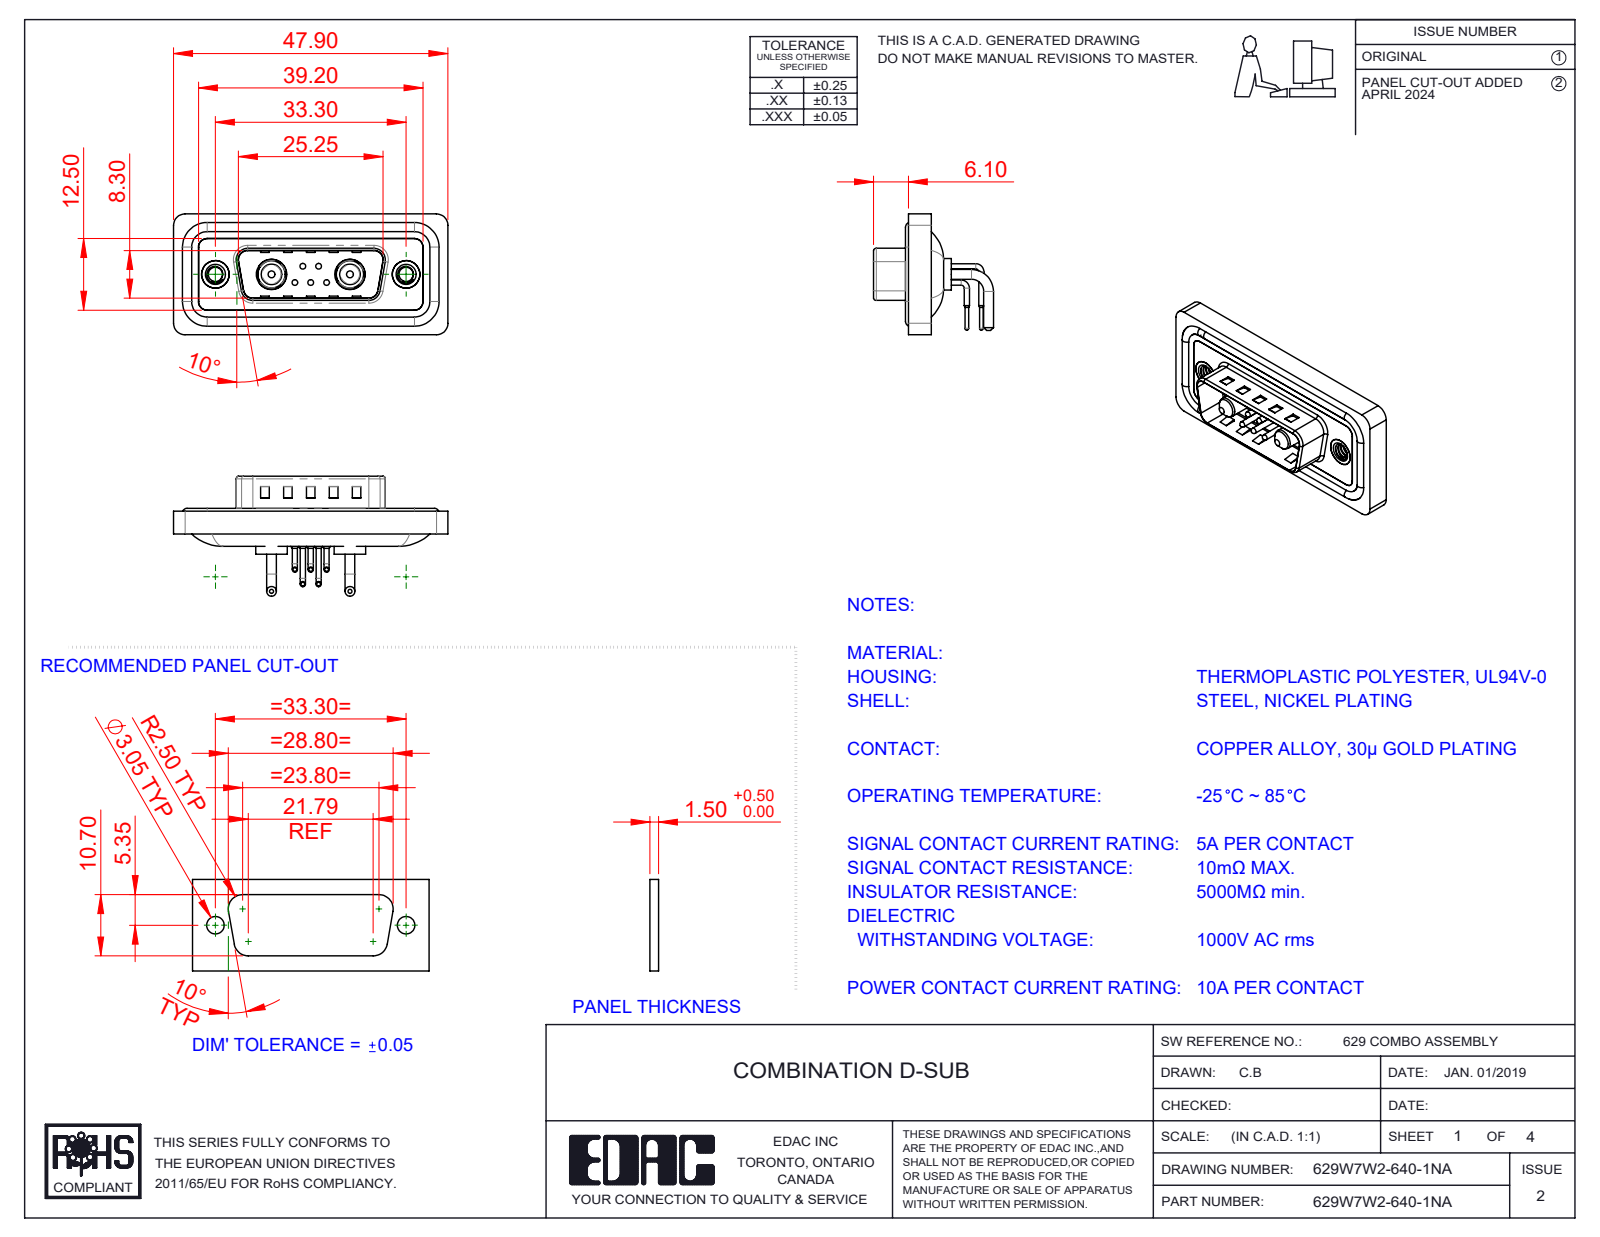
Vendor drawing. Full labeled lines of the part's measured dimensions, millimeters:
Part name (STEP PRODUCT): 629Combo Waterproof Housing_15 Contacts; 629Combo Shell Rear_15 Contacts; 629Combo Contact Row 2; Power Pin_10A RA (+5 more)
STEP written by: SolidWorks 2023 (CONFIG_CONTROL_DESIGN)
Units: millimetres
Bodies: 16 solids, 1077 faces (517 planar, 404 cylindrical, 156 other)
Overall size (bounding box): 47.9 × 21.1 × 20.95
Volume: 5 568 mm³ · Surface area: 9 043 mm²
Round holes (diameter × count): ⌀0.75 ×5, ⌀1.6 ×5, ⌀2 ×5, ⌀2.5 ×2, ⌀4 ×2, ⌀4.8 ×2, ⌀4.85 ×2, ⌀5 ×2, ⌀5.3 ×2
Round bosses / shafts (diameter × count): ⌀0.9 ×10, ⌀1.5 ×5, ⌀1 ×5, ⌀0.65 ×5, ⌀1.7 ×4, ⌀1.6 ×4, ⌀5.5 ×2, ⌀5.2 ×2
Partial cylindrical surfaces — rounded edges, fillets, slot ends (radius × count): R2 ×20, R1.5 ×18, R0.5 ×8, R1.6 ×8, R1.01 ×5, R0.25 ×4, R0.6 ×4, R0.65 ×4
Main face-to-face distances: 0.4, 2.9, 0.8, 1.1, 2.1, 1.6, 2.5, 3.1, 4.5, 4.1
Hole centre spacings: 3.16, 2.77, 9.8, 23.5, 4.31, 4.33, 5.03, 5.04
